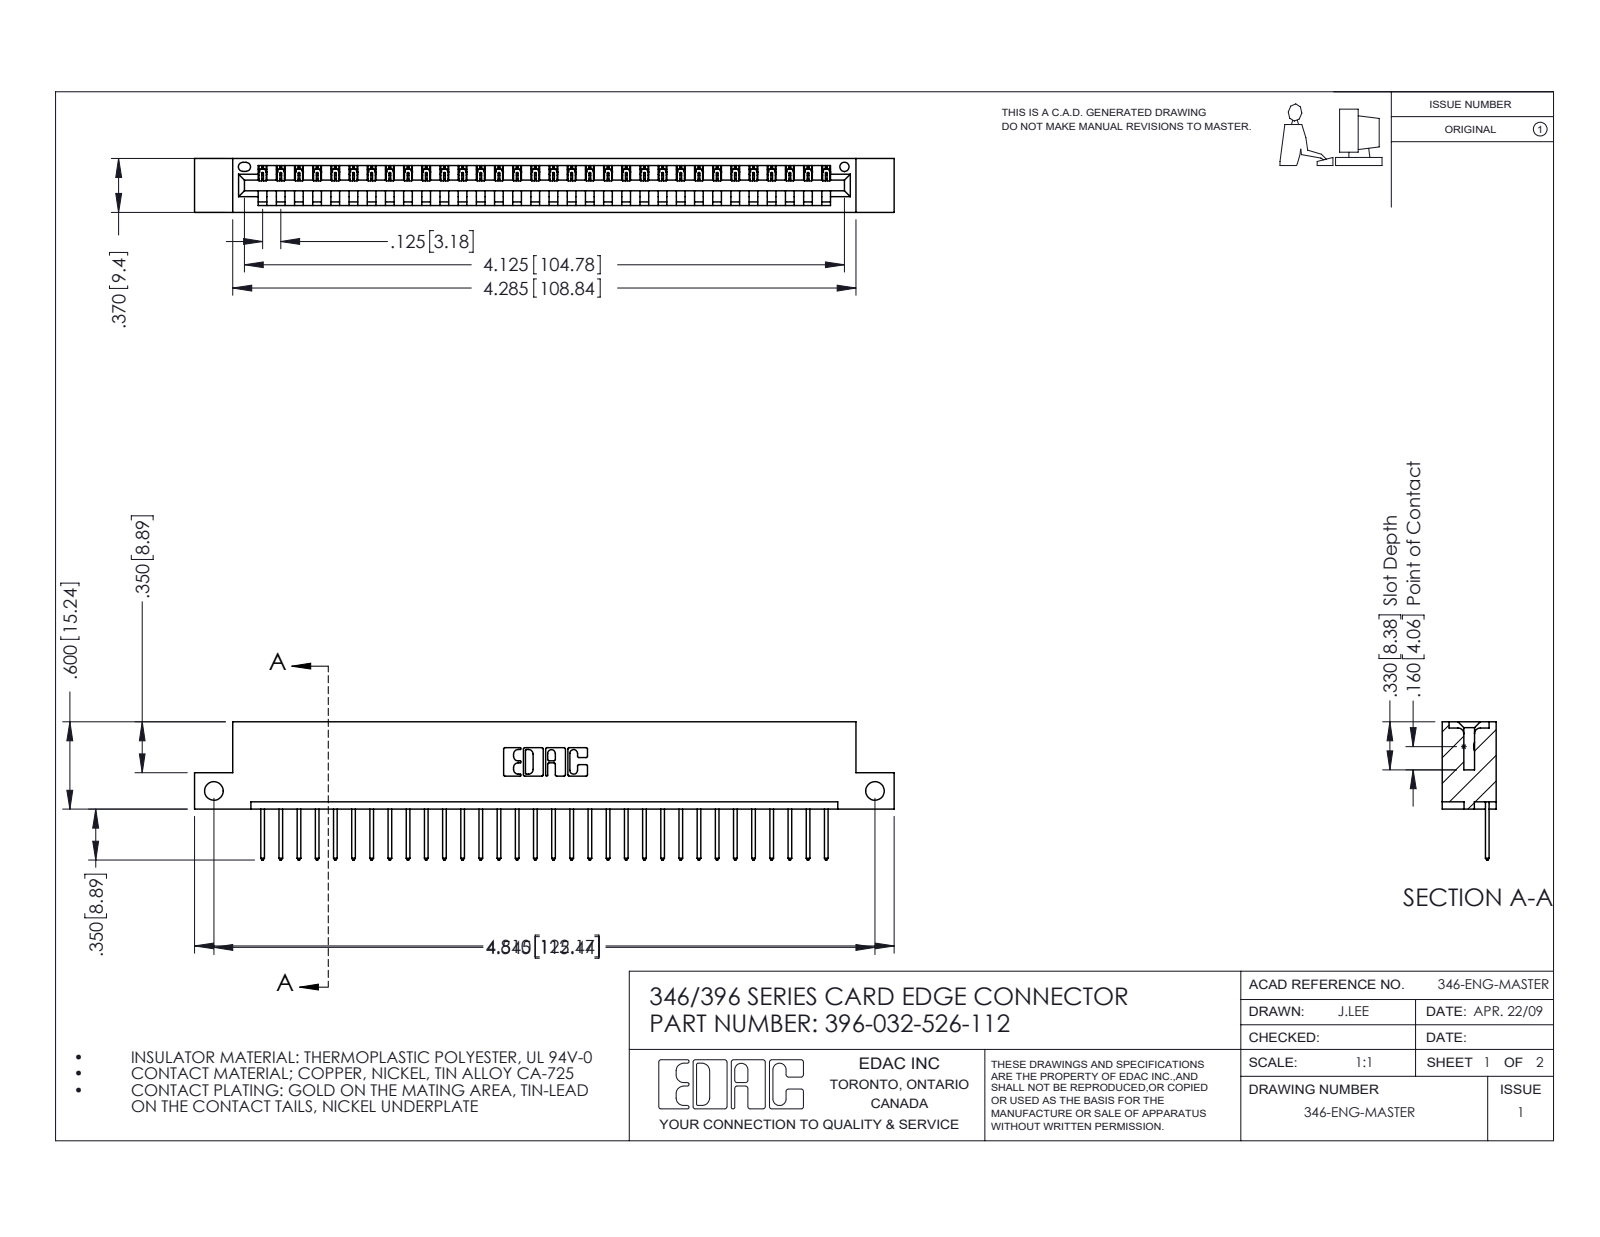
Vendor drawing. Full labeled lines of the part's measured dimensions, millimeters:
Part name (STEP PRODUCT): 345-292-001_345-293-126; 396-032-526-112; 346 Part_Flush Mounting Lugs - Side Mount
STEP written by: SolidWorks 2016 (CONFIG_CONTROL_DESIGN)
Units: millimetres
Bodies: 33 solids, 1978 faces (1356 planar, 622 cylindrical, 0 other)
Overall size (bounding box): 122.2 × 24.1 × 9.4
Volume: 11 500 mm³ · Surface area: 14 100 mm²
Round holes (diameter × count): ⌀3.3 ×2, ⌀1.6 ×1
Partial cylindrical surfaces — rounded edges, fillets, slot ends (radius × count): R0.2 ×64, R0.3 ×64, R0.3 ×22, R0.2 ×6, R0.8 ×6, R0.7 ×3, R0.8 ×2, R1 ×2
Main face-to-face distances: 1.2, 8.2, 9.4, 6.4, 1.8, 7.6, 0.6, 3.8, 5.6, 2.5
Hole centre spacings: 115.4
